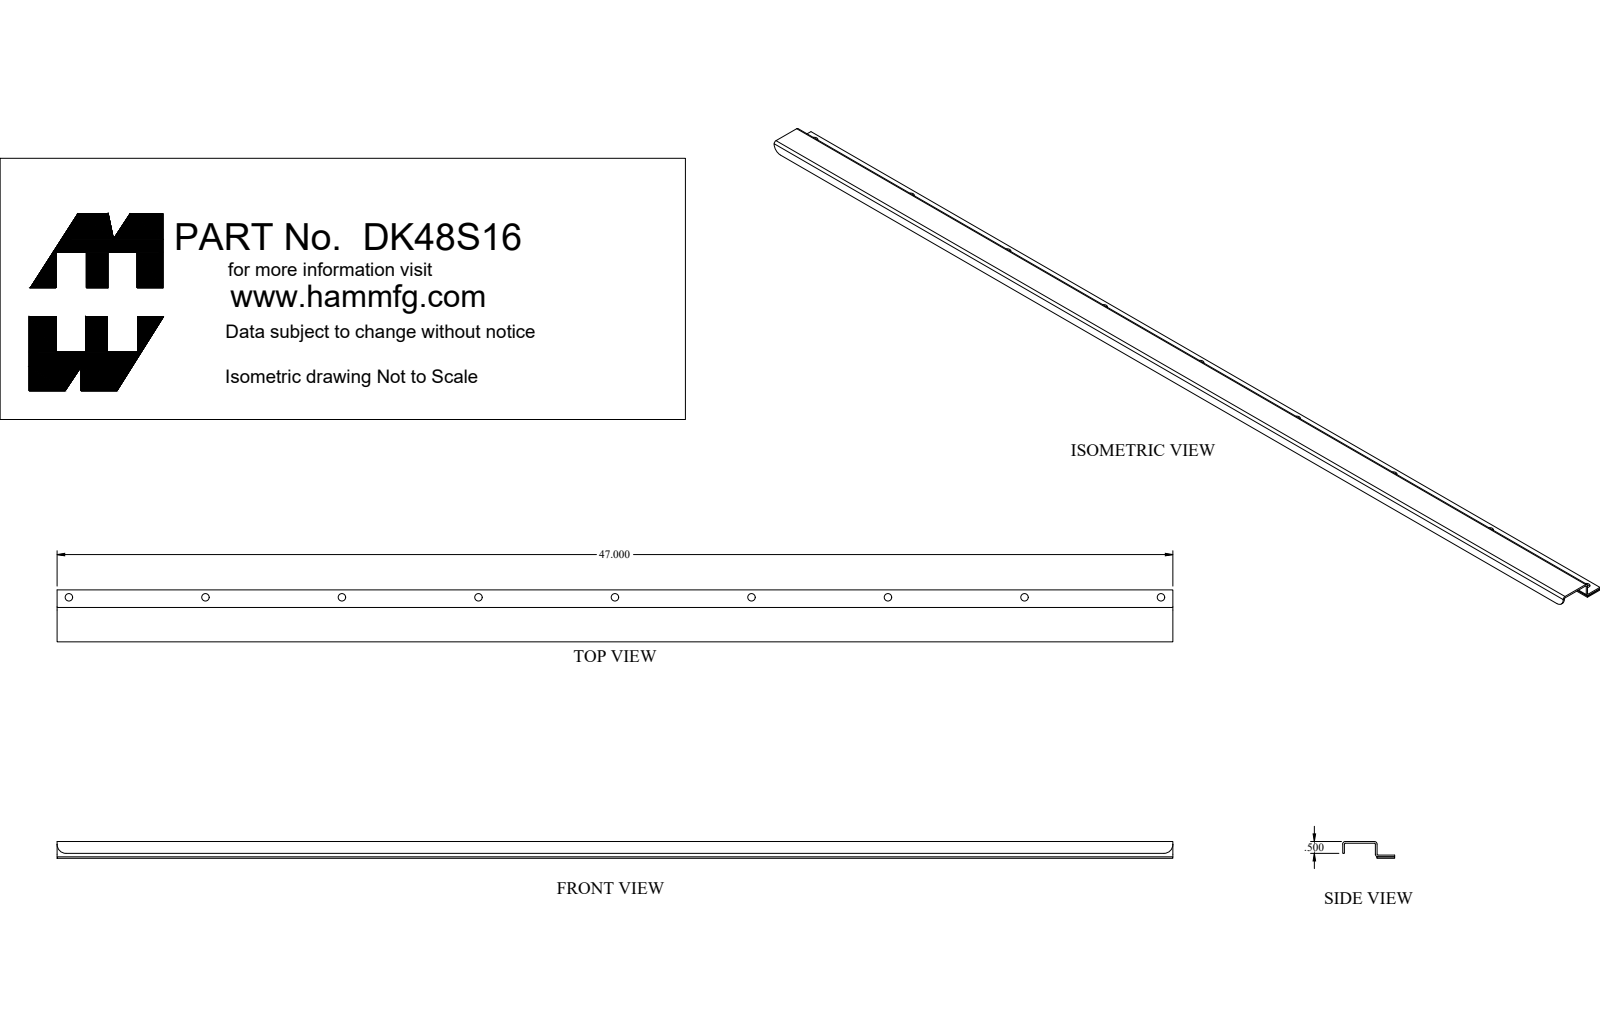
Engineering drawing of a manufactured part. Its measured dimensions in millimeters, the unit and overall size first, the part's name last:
Units: millimetres
Overall size (bounding box): 1193.8 × 55.6 × 33.6
Round holes (diameter × count): ⌀8 ×9, ⌀5 ×1, ⌀7 ×1
Round bosses / shafts (diameter × count): ⌀15.9 ×1, ⌀12.3 ×1, ⌀6.4 ×1
Partial cylindrical surfaces — rounded edges, fillets, slot ends (radius × count): R0.9 ×3, R2.7 ×3, R9.5 ×2
Main face-to-face distances: 1.8, 14.5, 16.4, 1.6, 35, 12.7, 16.1, 18, 3.4, 36.8
Hole centre spacings: 146.1, 292.1, 438.2, 584.2, 730.3, 876.3, 1022.4, 1168.4
Volume: 208 600 mm³ · Surface area: 242 800 mm²
Bodies: 5 solids, 70 faces (47 planar, 22 cylindrical, 1 other)
Part name (STEP PRODUCT): DK48S16
STEP written by: SolidWorks 2021 (AUTOMOTIVE_DESIGN)
